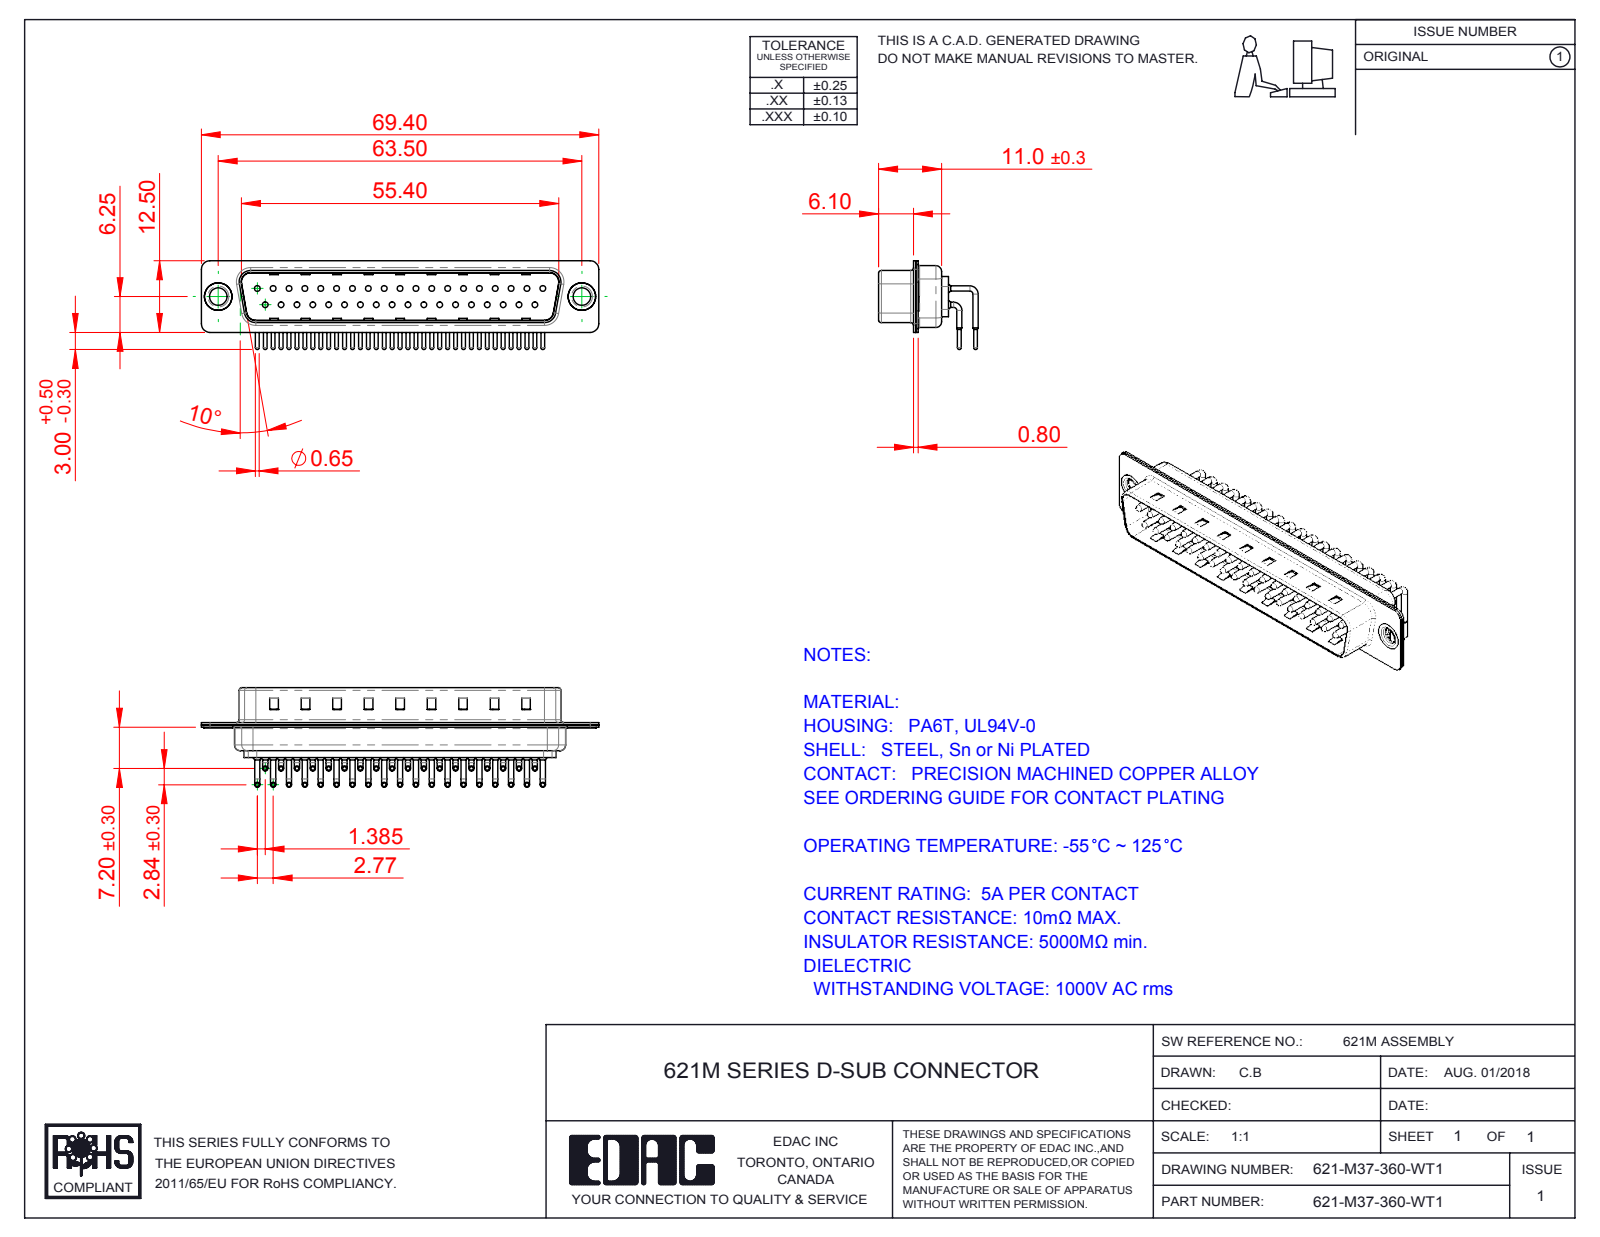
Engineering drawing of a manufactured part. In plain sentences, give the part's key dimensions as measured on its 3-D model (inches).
The part is named "621M Contact Row 1; 621-M37-360-WT1; 621M Shell Rear_37 Contacts; 621M Shell Front_37 Contacts (+3 more)". Its 3-D file was written by "SolidWorks 2016 (CONFIG_CONTROL_DESIGN)". It is 42 solids with 4456 faces: 2571 planar, 1457 cylindrical and 428 other. Overall it measures 2.732 by 0.685 by 0.61 inches. Its volume is 0.239 cubic inches and its surface area 15.84 square inches. Round holes: 37 of diameter 0.039, 37 of diameter 0.067, 37 of diameter 0.079, 2 of diameter 0.12, 2 of diameter 0.157, 2 of diameter 0.189. Round bosses or shafts: 74 of diameter 0.035, 37 of diameter 0.059, 37 of diameter 0.026, 2 of diameter 0.197, 2 of diameter 0.193, 2 of diameter 0.14. Partial cylindrical surfaces (rounded edges, fillets, slot ends): 37 of radius 0.04, 16 of radius 0.059, 12 of radius 0.079, 8 of radius 0.02, 8 of radius 0.063, 4 of radius 0.01, 4 of radius 0.024, 4 of radius 0.026. The main face-to-face distances are 0.016, 0.033, 0.376, 0.343, 0.049, 0.409, 0.059, 0.075, 0.014, 0.392. The hole center spacings are 0.124, 0.109, 0.218, 0.327, 0.198, 0.398, 0.436, 0.503.
